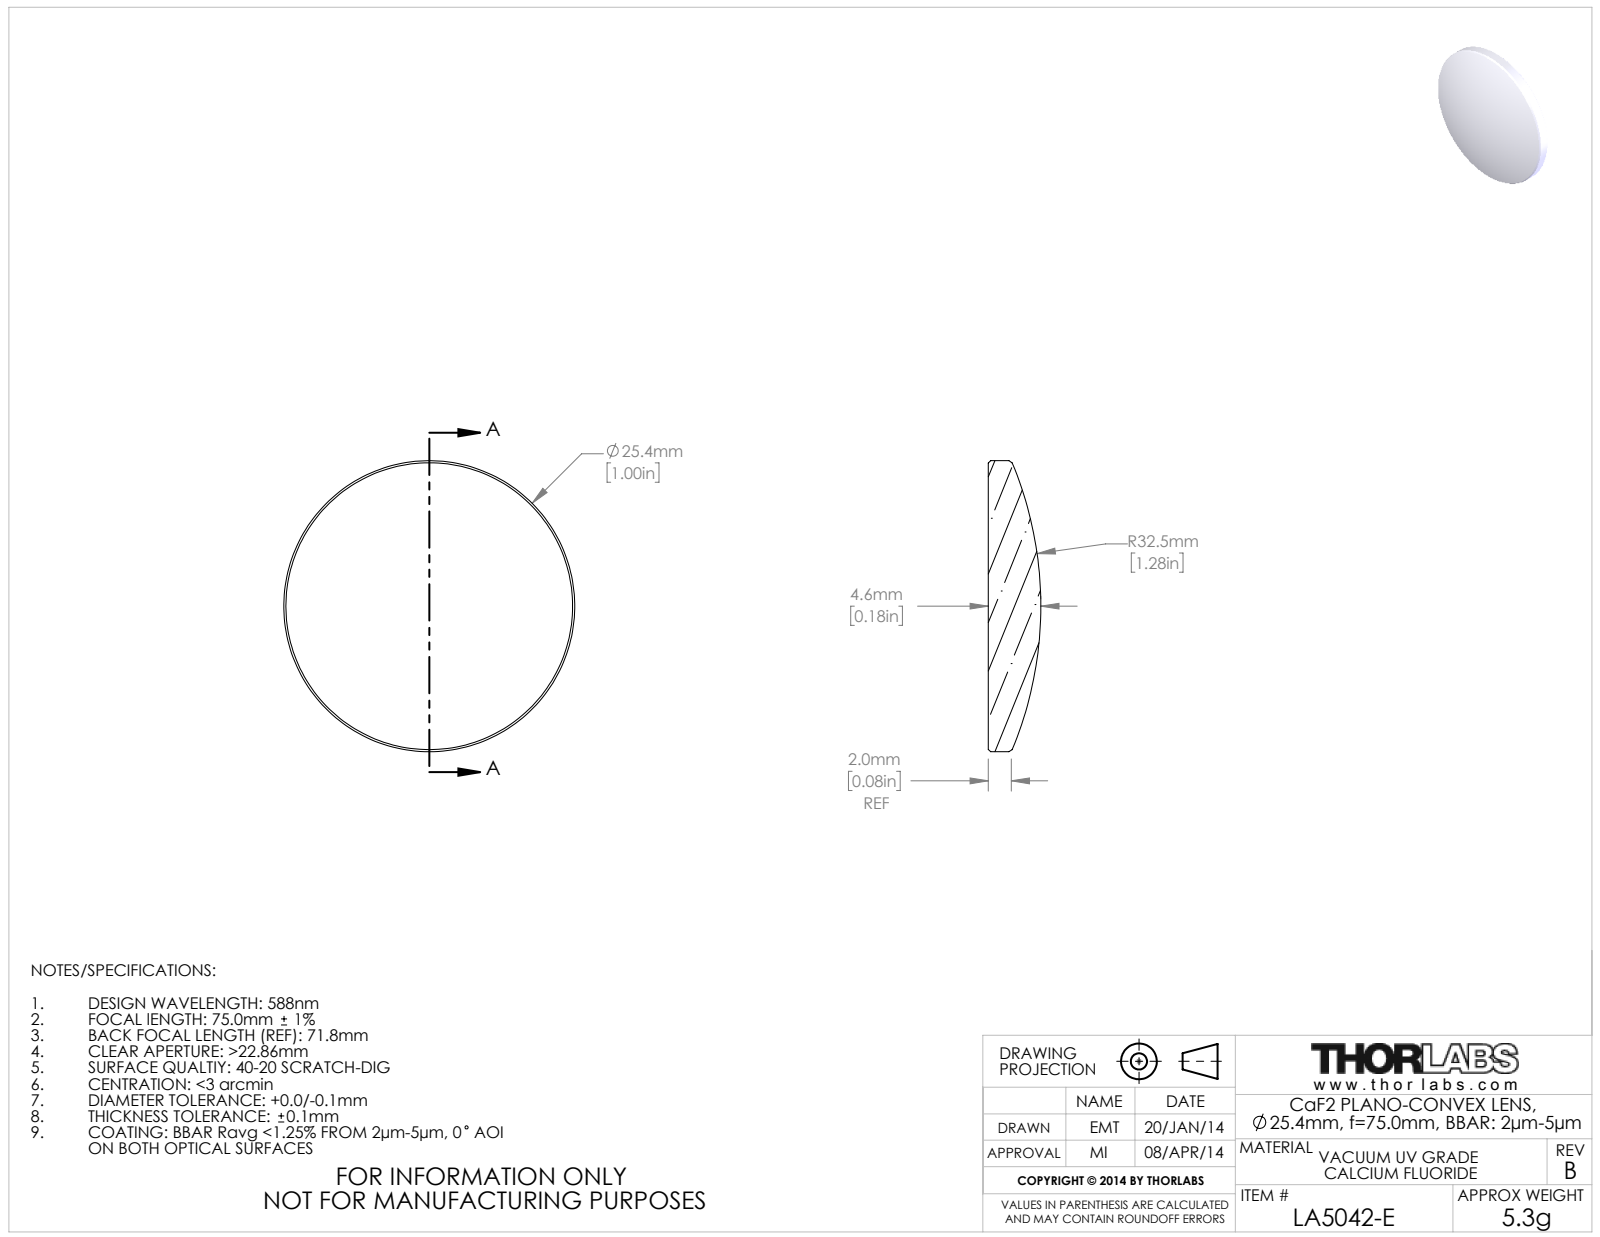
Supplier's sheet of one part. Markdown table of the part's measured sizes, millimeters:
| quantity | value |
| --- | --- |
| part name | 20133-E0W |
| STEP written by | SolidWorks 2018 (CONFIG_CONTROL_DESIGN) |
| units | millimeters |
| bodies | 1 solid, 9 faces (1 planar, 2 cylindrical, 6 other) |
| overall size | 25.4 × 25.4 × 4.58 |
| volume | 1 673 mm³ |
| surface area | 1 179 mm² |
| round bosses / shafts (diameter × count) | 25.4 × 1 |
